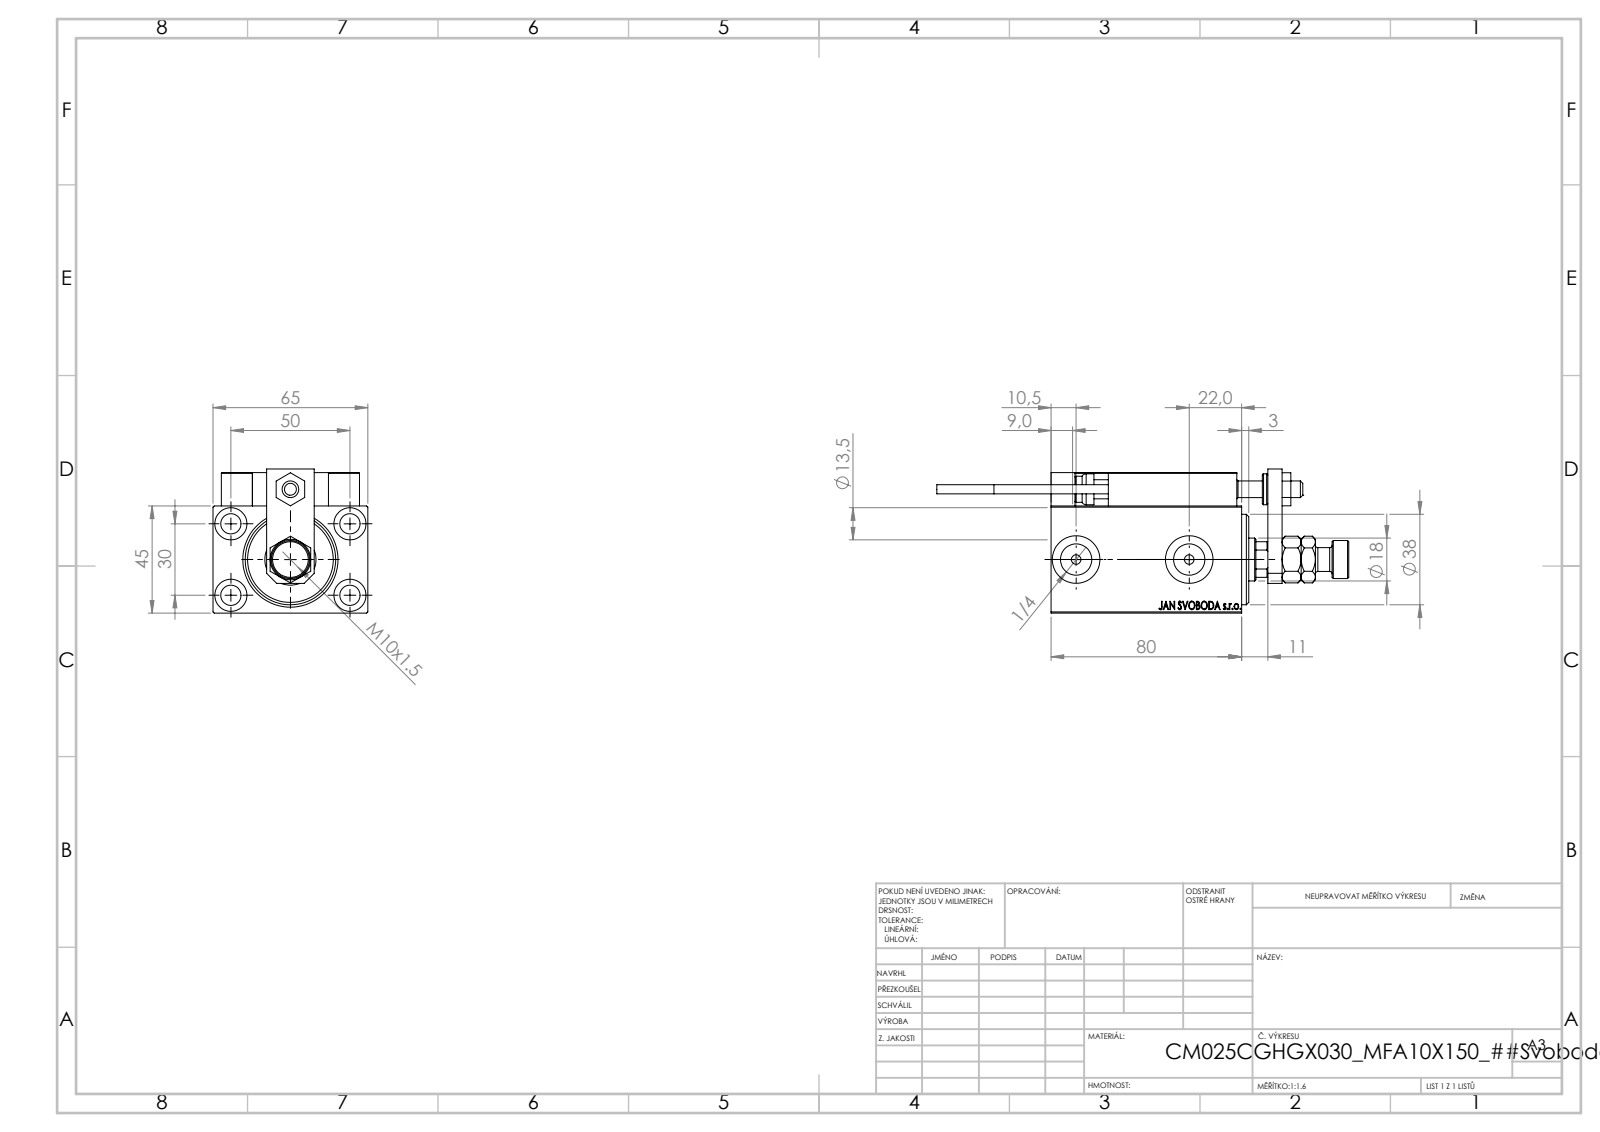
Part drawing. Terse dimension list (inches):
name: SWITCH DIM B,W; KONCOVKA; ALLEN BOLT D8; SWITCH_X_FRONT_BACK (+7 more)
written by: SolidWorks 2019 (CONFIG_CONTROL_DESIGN)
unit: in
bodies: 24 solids, 1334 faces (576 planar, 192 cylindrical, 566 other)
size: 6.811 × 2.559 × 2.382
volume: 15.48 in³; area: 118 in²
holes: 6× ⌀0.157, 5× ⌀0.315, 5× ⌀0.335, 4× ⌀0.126, 4× ⌀0.531, 2× ⌀0.197, 2× ⌀0.518, 2× ⌀0.787, 1× ⌀0.276, 1× ⌀0.571, 1× ⌀0.709, 1× ⌀0.846
bosses: 2× ⌀0.197, 2× ⌀0.15, 1× ⌀0.63, 1× ⌀0.512, 1× ⌀0.433, 1× ⌀0.394
rounds: 30× R0.012, 2× R0.118, 1× R0.335
face distances: 1.772, 0.551, 2.559, 2.323, 0.236, 0.118, 3.583, 0.512, 0.138, 0.197
hole spacings: 1.148, 0.448, 0.787, 1.138, 1.165, 1.169, 1.181, 1.262
